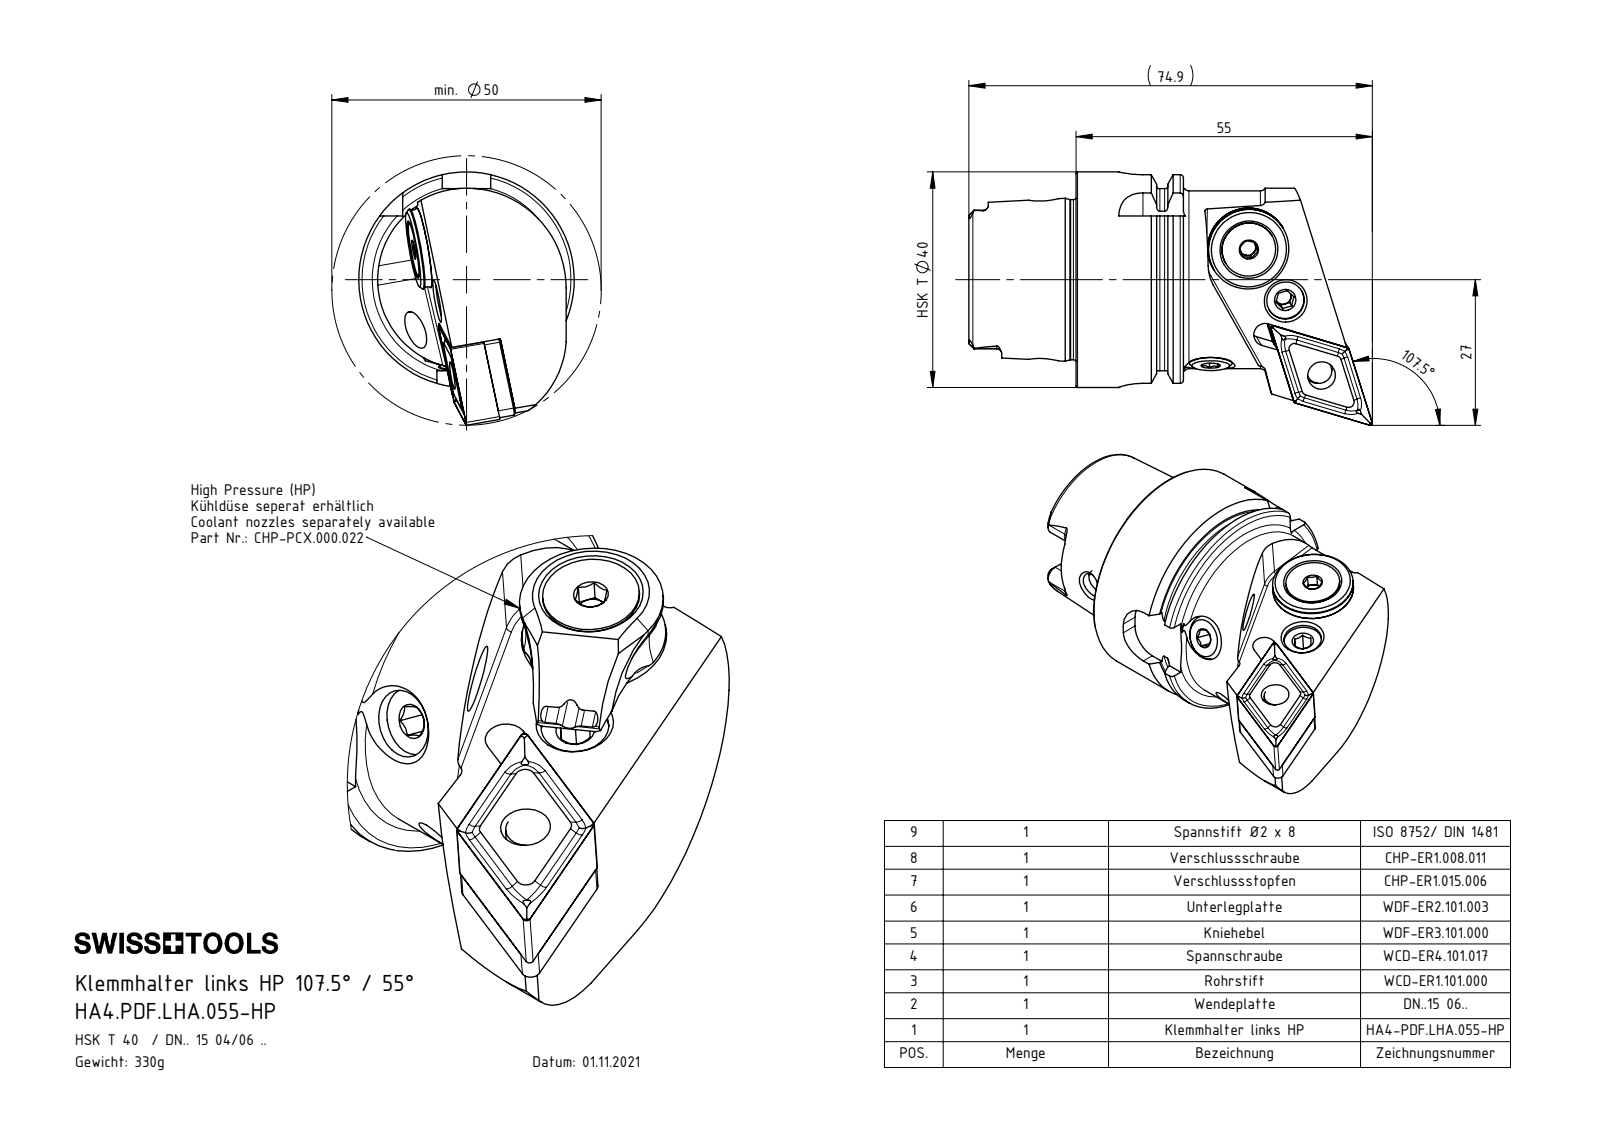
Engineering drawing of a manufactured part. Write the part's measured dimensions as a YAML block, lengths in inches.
part_name: "WDF-ER2.101.003_A; HA4.PDF.LHA.055-HP; KVT_MB_600_040; DIN 7991 - M5x18 (+8 more)"
step_written_by: "SolidWorks 2022 (AUTOMOTIVE_DESIGN)"
units: inches
bodies: {solids: 14, faces: 632, planar: 169, cylindrical: 182, other: 281}
overall_size: [2.949, 1.85, 1.575]
volume: 2.676
surface_area: 31.25
round_holes:
  - {diameter: 0.13, count: 3}
  - {diameter: 0.118, count: 2}
  - {diameter: 0.197, count: 2}
  - {diameter: 0.276, count: 2}
  - {diameter: 0.047, count: 1}
  - {diameter: 0.079, count: 1}
  - {diameter: 0.157, count: 1}
  - {diameter: 0.165, count: 1}
  - {diameter: 0.181, count: 1}
  - {diameter: 0.203, count: 1}
  - {diameter: 0.209, count: 1}
  - {diameter: 0.256, count: 1}
round_bosses_or_shafts:
  - {diameter: 0.315, count: 2}
  - {diameter: 1.575, count: 1}
  - {diameter: 1.368, count: 1}
  - {diameter: 1.299, count: 1}
  - {diameter: 1.17, count: 1}
  - {diameter: 0.585, count: 1}
  - {diameter: 0.528, count: 1}
  - {diameter: 0.394, count: 1}
partial_cylinders:
  - {radius: 0.039, count: 7}
  - {radius: 0.035, count: 6}
  - {radius: 0.016, count: 4}
  - {radius: 0.02, count: 4}
  - {radius: 0.177, count: 4}
  - {radius: 0.047, count: 3}
  - {radius: 0.098, count: 3}
  - {radius: 0.197, count: 3}
face_to_face_distances: [0.238, 0.012, 0.125, 0.363, 0.487, 0.313, 0.5, 0.785, 0.472, 0.177]
hole_center_spacings: [0.177, 0.975, 0.362, 0.615, 1.097, 1.097, 0.486, 0.487]
